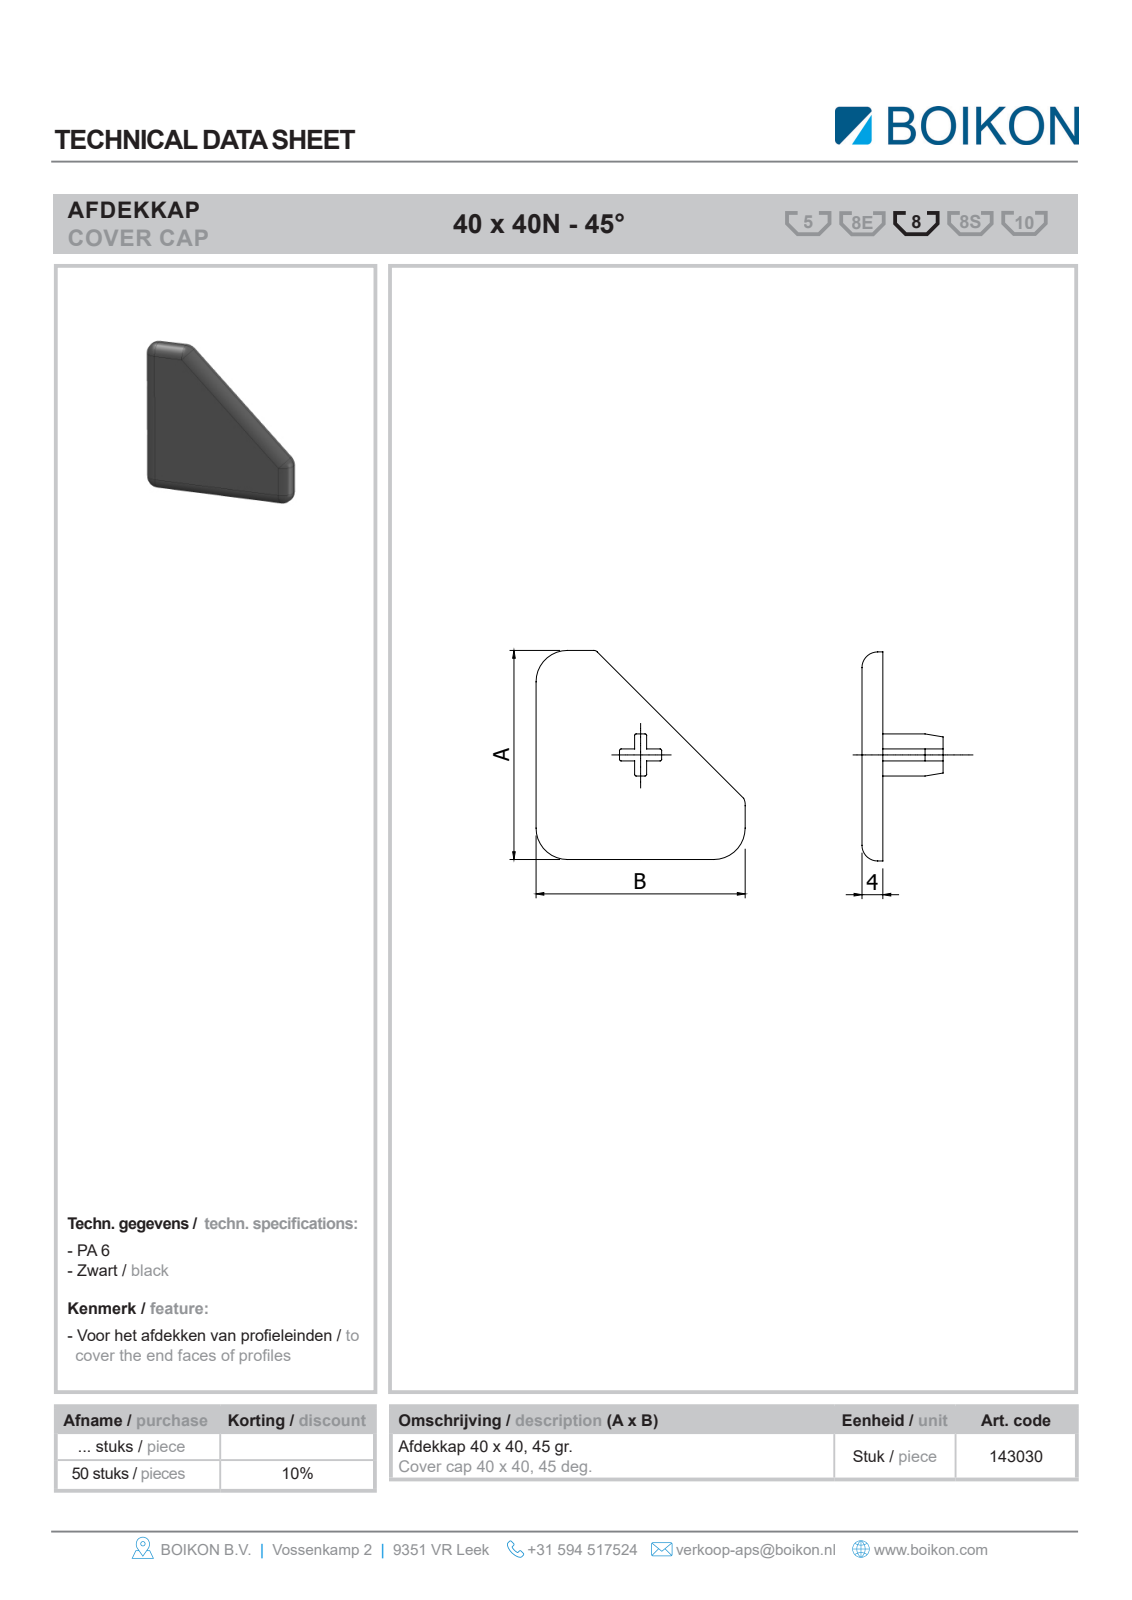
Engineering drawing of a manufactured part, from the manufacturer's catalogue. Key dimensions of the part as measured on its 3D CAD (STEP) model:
Part name (STEP PRODUCT): Root; 143030 Afdekkap 40 x 40-45gr.BOIKON
STEP written by: HiCAD 2013 1802.4 Build 509 (AUTOMOTIVE_DESIGN)
Units: millimetres
Bodies: 1 solid, 22 faces (7 planar, 10 cylindrical, 5 other)
Overall size (bounding box): 40 × 40 × 4
Volume: 4 514 mm³ · Surface area: 2 761 mm²
Partial cylindrical surfaces — rounded edges, fillets, slot ends (radius × count): R3 ×10
Main face-to-face distances: 4, 40
